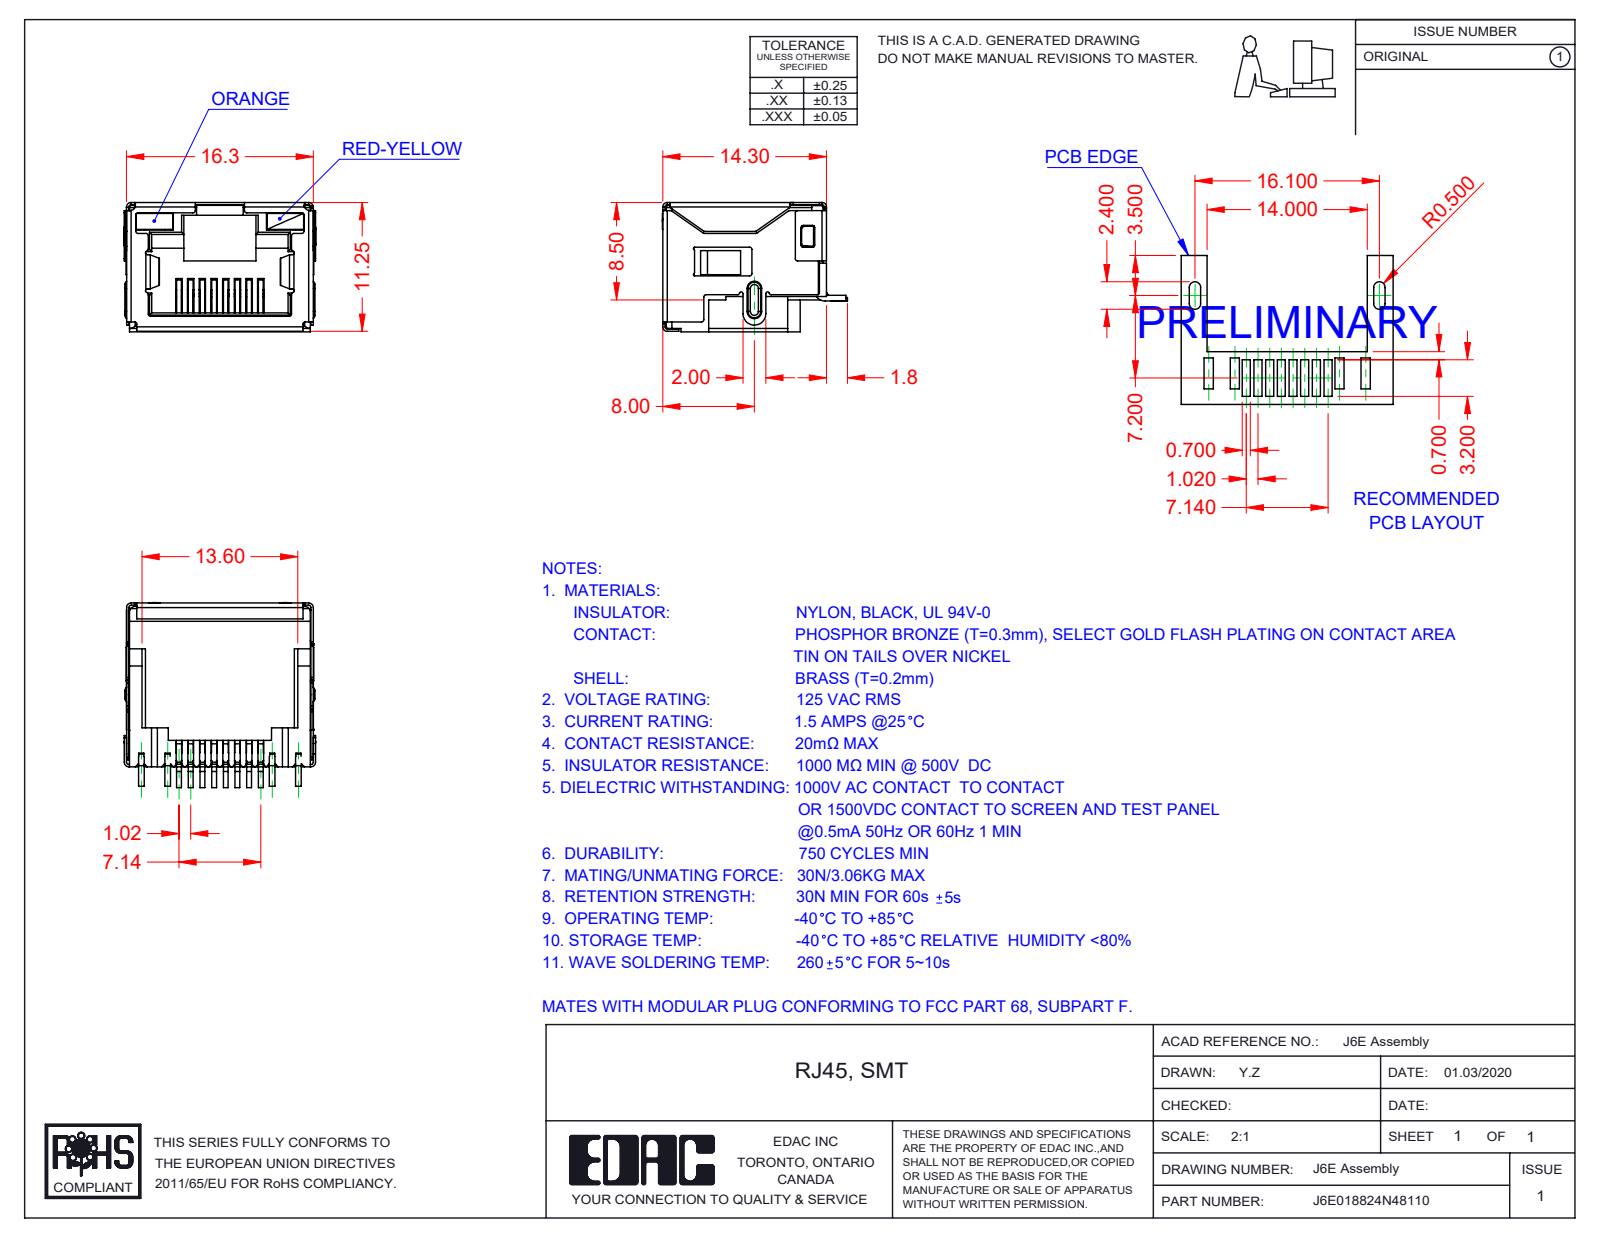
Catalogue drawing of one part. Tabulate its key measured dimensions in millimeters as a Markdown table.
| quantity | value |
| --- | --- |
| part name | J6E018824N48110; 6E LED RH_8-Red-Yellow; 6E Shield_LED; 6E Contacts (+2 more) |
| STEP written by | SolidWorks 2016 (CONFIG_CONTROL_DESIGN) |
| units | millimeters |
| bodies | 12 solids, 1498 faces (1099 planar, 349 cylindrical, 50 other) |
| overall size | 16.75 × 16.15 × 11.3 |
| volume | 1 109 mm³ |
| surface area | 4 045 mm² |
| partial cylindrical surfaces (radius × count) | 0.2 × 82, 0.25 × 17, 0.4 × 13, 0.5 × 13, 0.1 × 10, 0.15 × 7, 0.3 × 4, 1 × 3 |
| main face-to-face distances | 11.05, 16.05, 16.1, 15.85, 11.1, 11.3, 2.4, 0.7, 9.85, 0.49 |
